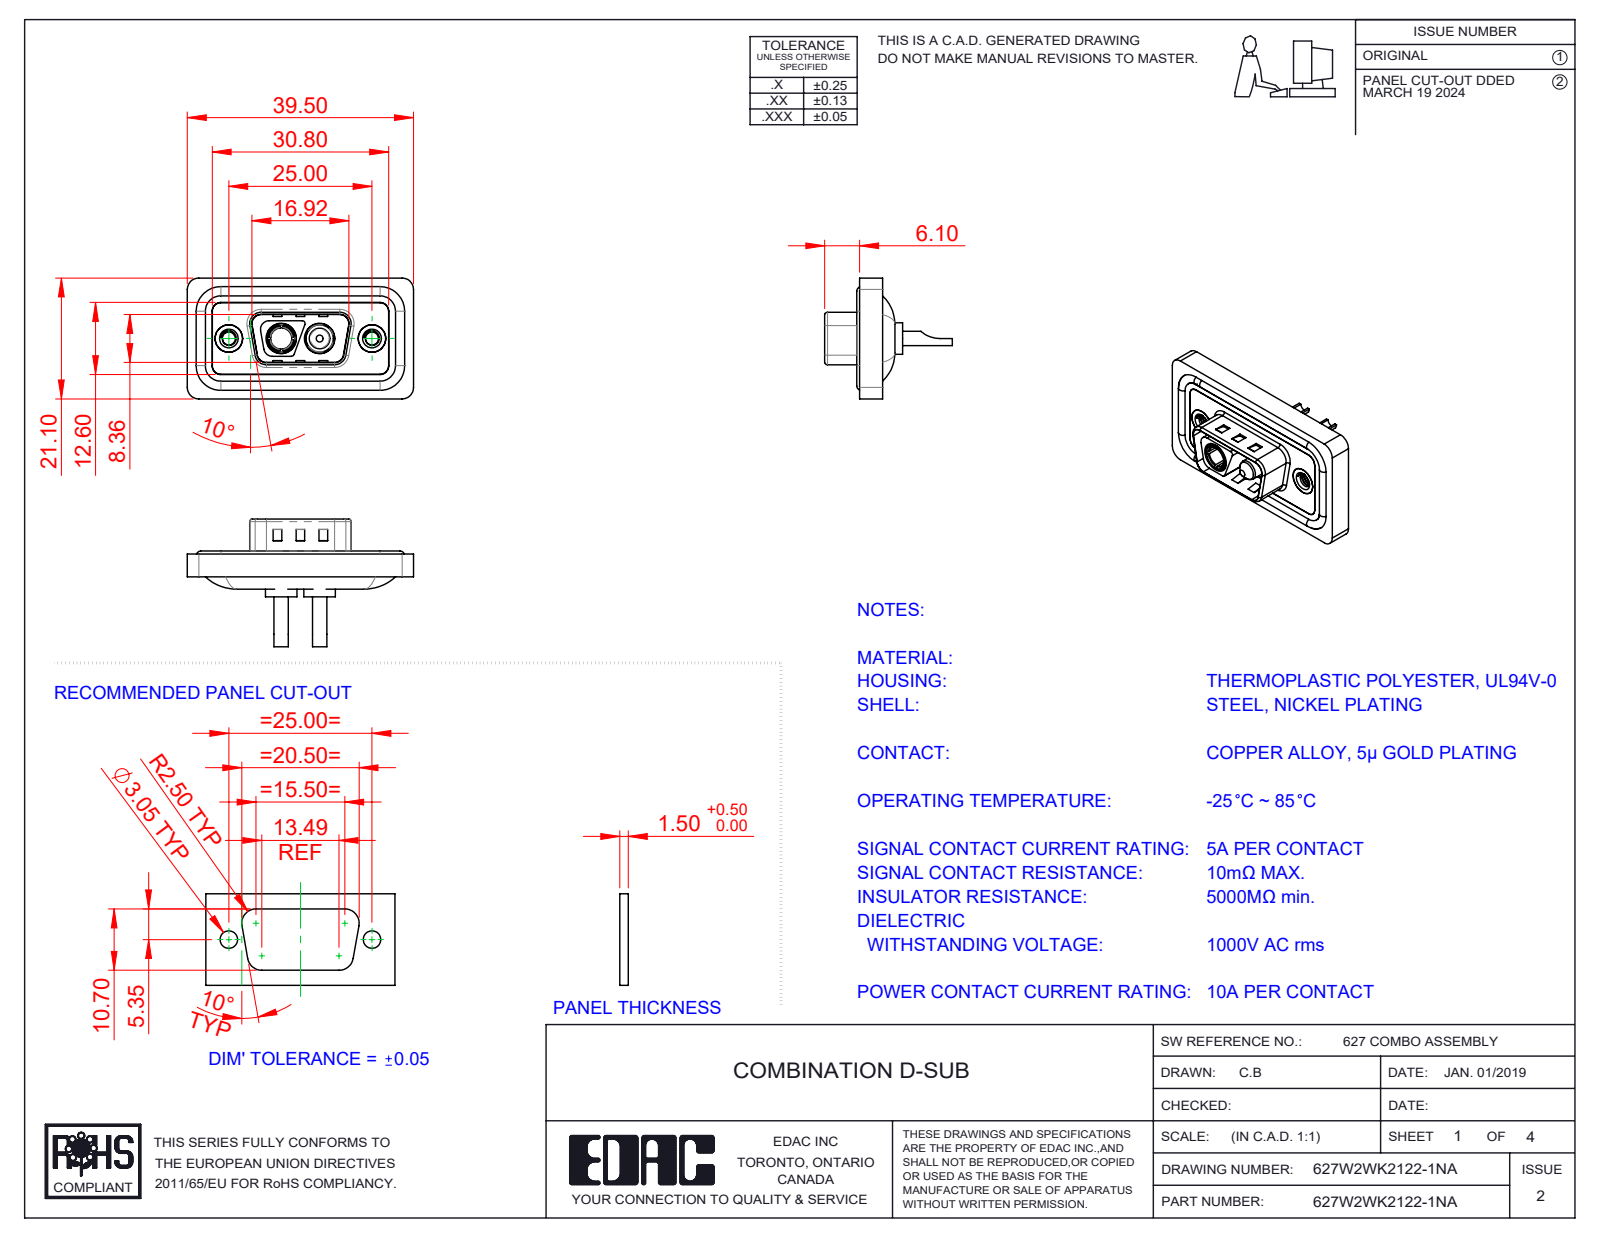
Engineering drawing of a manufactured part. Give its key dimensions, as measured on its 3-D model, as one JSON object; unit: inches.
{"part_name": "Power Pin_10A SC; 627Combo Waterproof Housing_09 Contacts; 627Combo Shell Rear_09 Contacts; 627Combo Housing_2WK2 (+4 more)", "step_written_by": "SolidWorks 2023 (CONFIG_CONTROL_DESIGN)", "units": "inches", "bodies": {"solids": 11, "faces": 543, "planar": 193, "cylindrical": 235, "other": 115}, "overall_size": [1.555, 0.878, 0.831], "volume_in3": 0.278, "surface_area_in2": 11.52, "round_holes": [[0.067, 2], [0.089, 2], [0.157, 2], [0.189, 2], [0.191, 2], [0.197, 2], [0.209, 2], [0.146, 1]], "round_bosses_or_shafts": [[0.063, 4], [0.217, 2], [0.205, 2], [0.193, 2], [0.187, 2], [0.148, 2], [0.098, 2], [0.195, 1]], "partial_cylinders_radius": [[0.059, 24], [0.079, 18], [0.02, 10], [0.063, 8], [0.01, 4], [0.024, 4], [0.026, 4], [0.035, 4]], "face_to_face_distances": [0.016, 0.043, 0.114, 0.02, 0.122, 0.063, 0.059, 0.157, 0.098, 0.071], "hole_center_spacings": [0.36, 0.624, 0.265, 0.984]}
